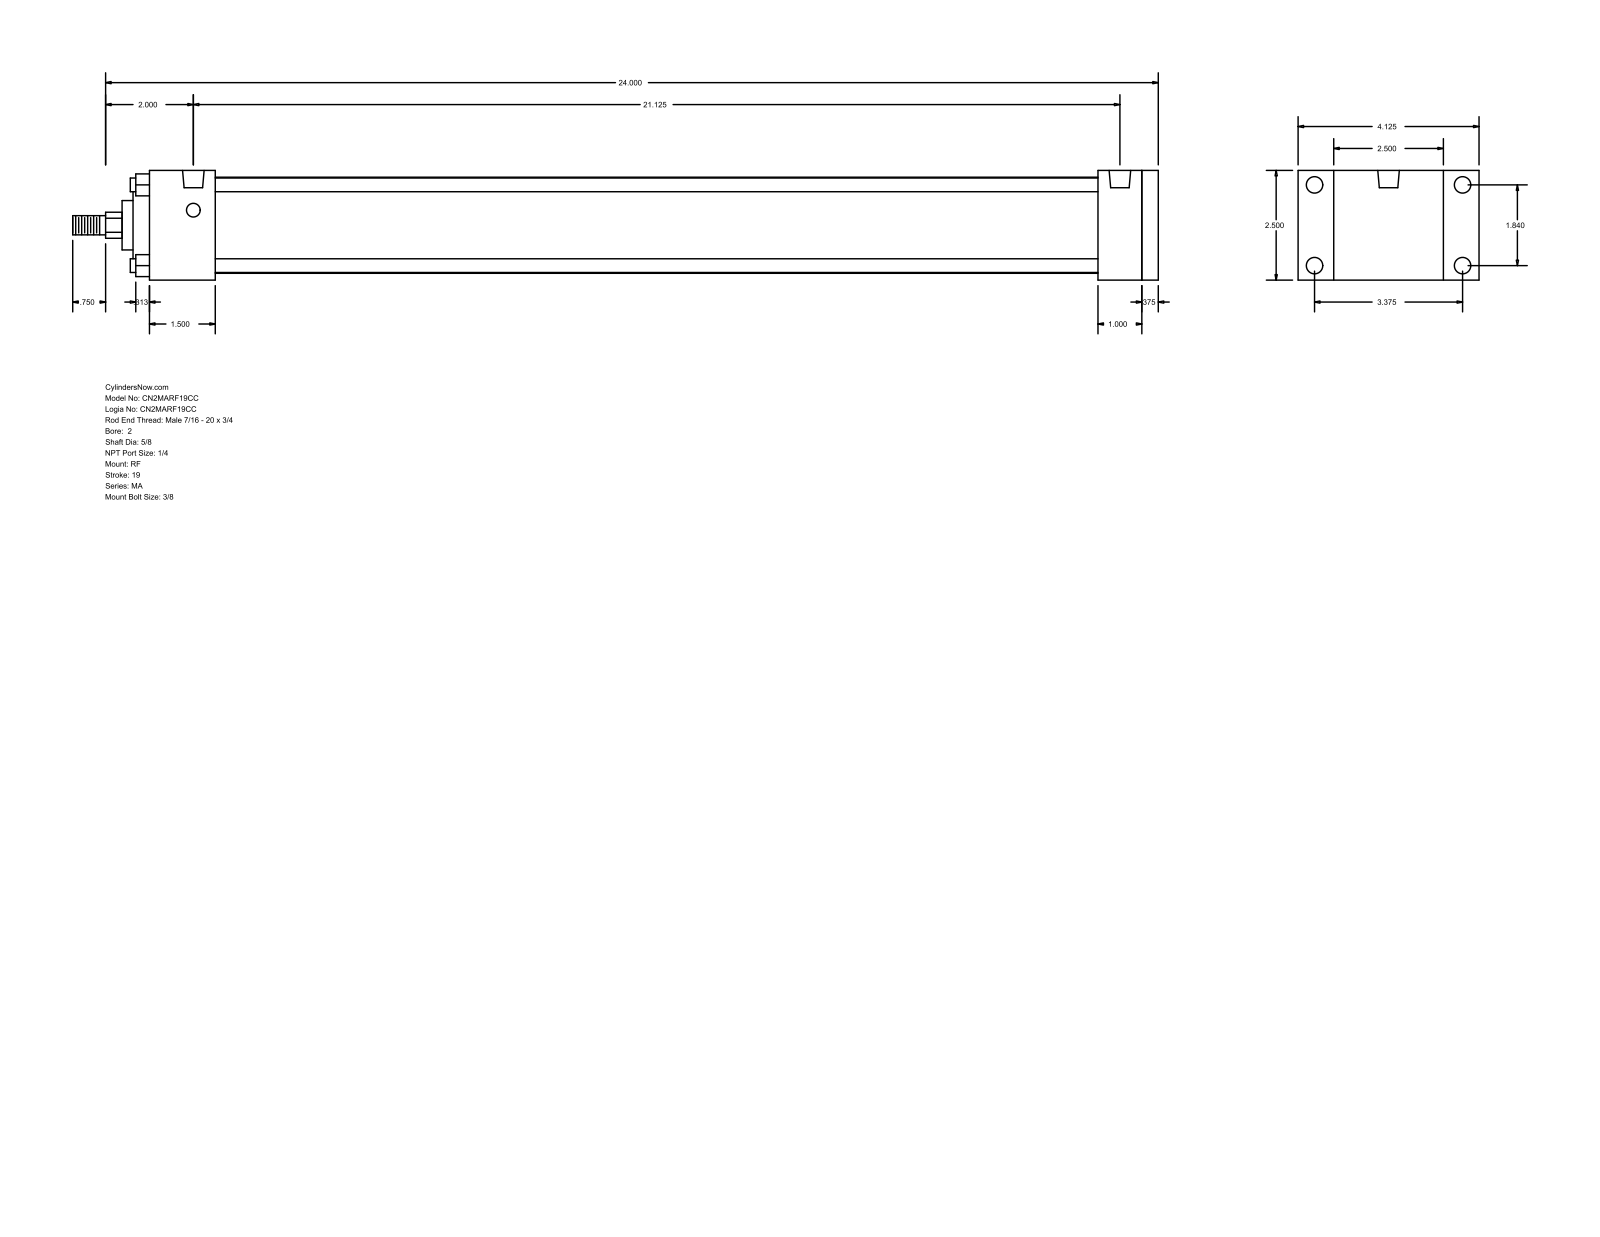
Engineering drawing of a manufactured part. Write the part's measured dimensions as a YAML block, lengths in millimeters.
part_name: "MA_RF__0200_0.625"
step_written_by: "GSSL Pune (CONFIG_CONTROL_DESIGN)"
units: millimeters
bodies: {solids: 0, faces: 94, planar: 65, cylindrical: 29, other: 0}
overall_size: [628.65, 104.78, 63.5]
round_holes:
  - {diameter: 7.94, count: 4}
  - {diameter: 9.53, count: 4}
  - {diameter: 12.49, count: 2}
round_bosses_or_shafts:
  - {diameter: 7.94, count: 4}
  - {diameter: 55.63, count: 1}
  - {diameter: 50.8, count: 1}
  - {diameter: 28.57, count: 1}
  - {diameter: 15.88, count: 1}
  - {diameter: 11.11, count: 1}
partial_cylinders:
  - {radius: 7.54, count: 1}
face_to_face_distances: [63.5, 9.52, 584.2, 38.1, 34.93, 593.72, 574.68, 536.58, 546.1, 549.27]
hole_center_spacings: [46.74, 85.72, 97.63, 536.58]
